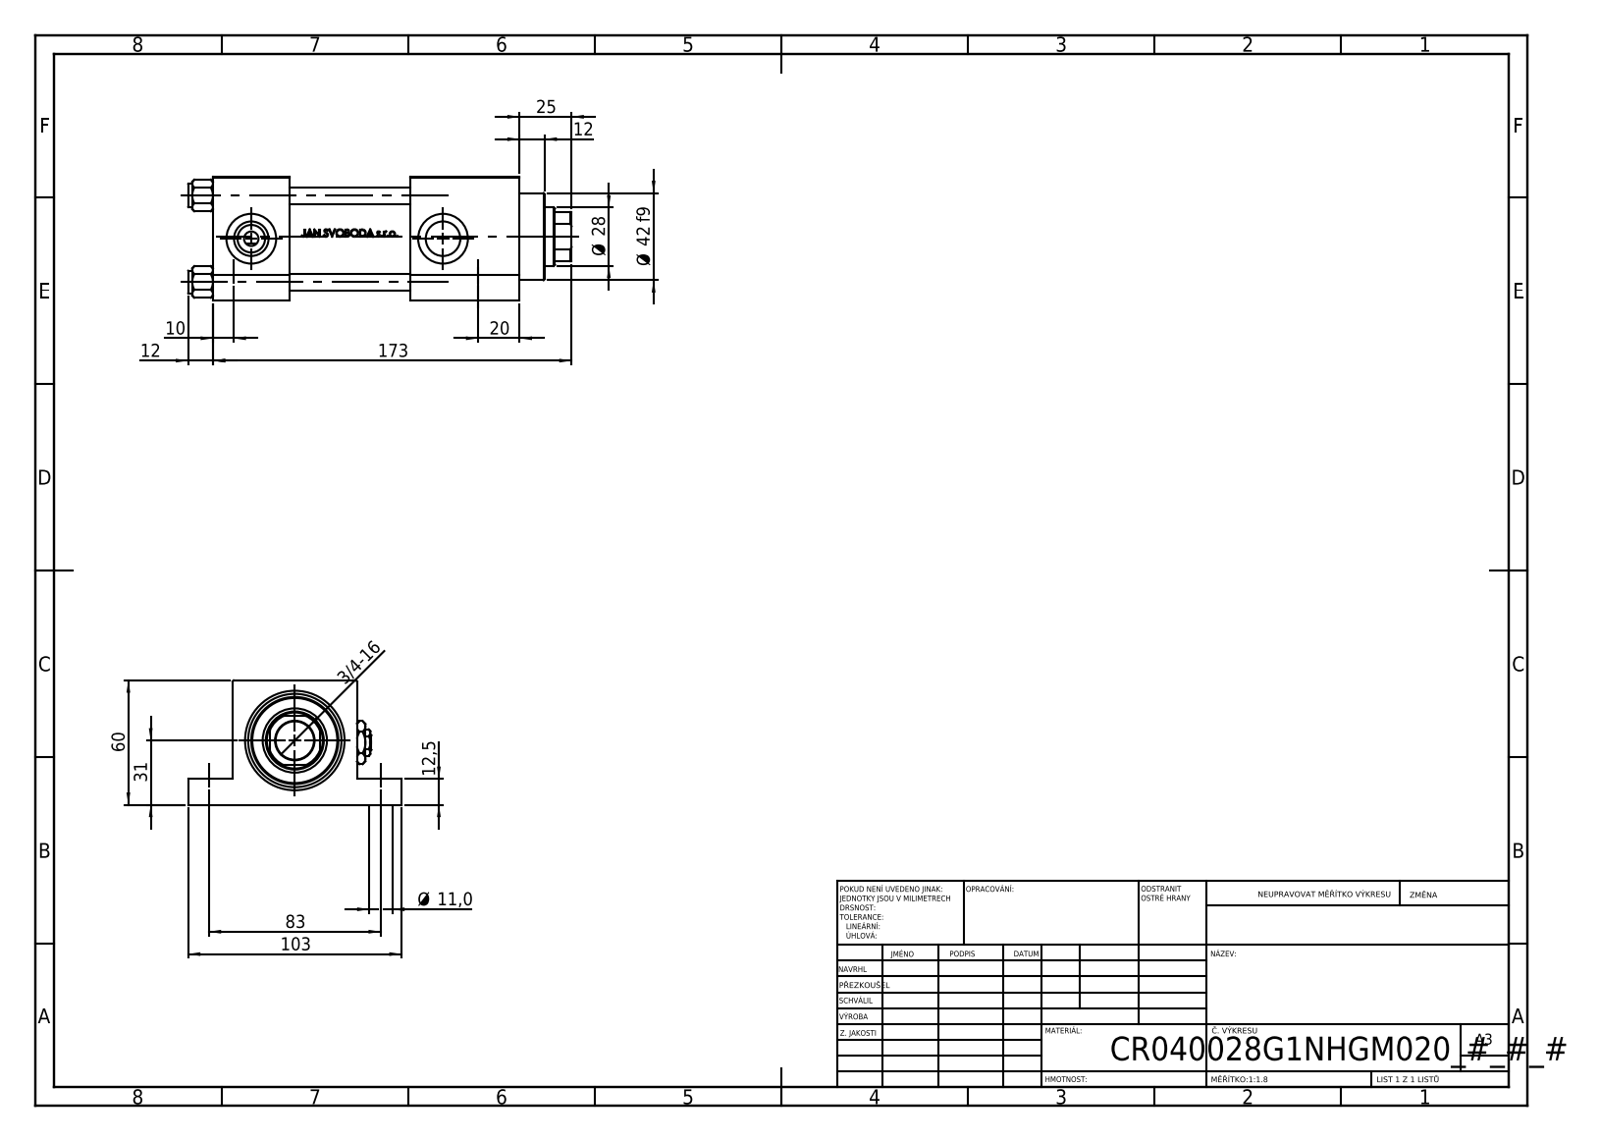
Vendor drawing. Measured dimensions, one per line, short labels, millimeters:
name: NUT_M5_G; V215CR_G_Body; Zatka_pro_OIL_PORT; V215_VC_A (+2 more)
written by: SolidWorks 2019 (CONFIG_CONTROL_DESIGN)
unit: mm
bodies: 12 solids, 1135 faces (455 planar, 128 cylindrical, 552 other)
size: 185 × 103 × 60
volume: 469 872 mm³; area: 121 527 mm²
holes: 4× ⌀8, 4× ⌀11, 2× ⌀7, 2× ⌀16.66, 2× ⌀24, 1× ⌀18.5, 1× ⌀28, 1× ⌀31, 1× ⌀40, 1× ⌀45
bosses: 4× ⌀11, 1× ⌀46, 1× ⌀42
rounds: 1× R13.5
face distances: 60, 37, 12.5, 47.5, 58, 95, 53, 148, 111, 21.5
hole spacings: 41.7, 28.79, 30.2, 58.97, 83, 118, 144.27, 92.5
